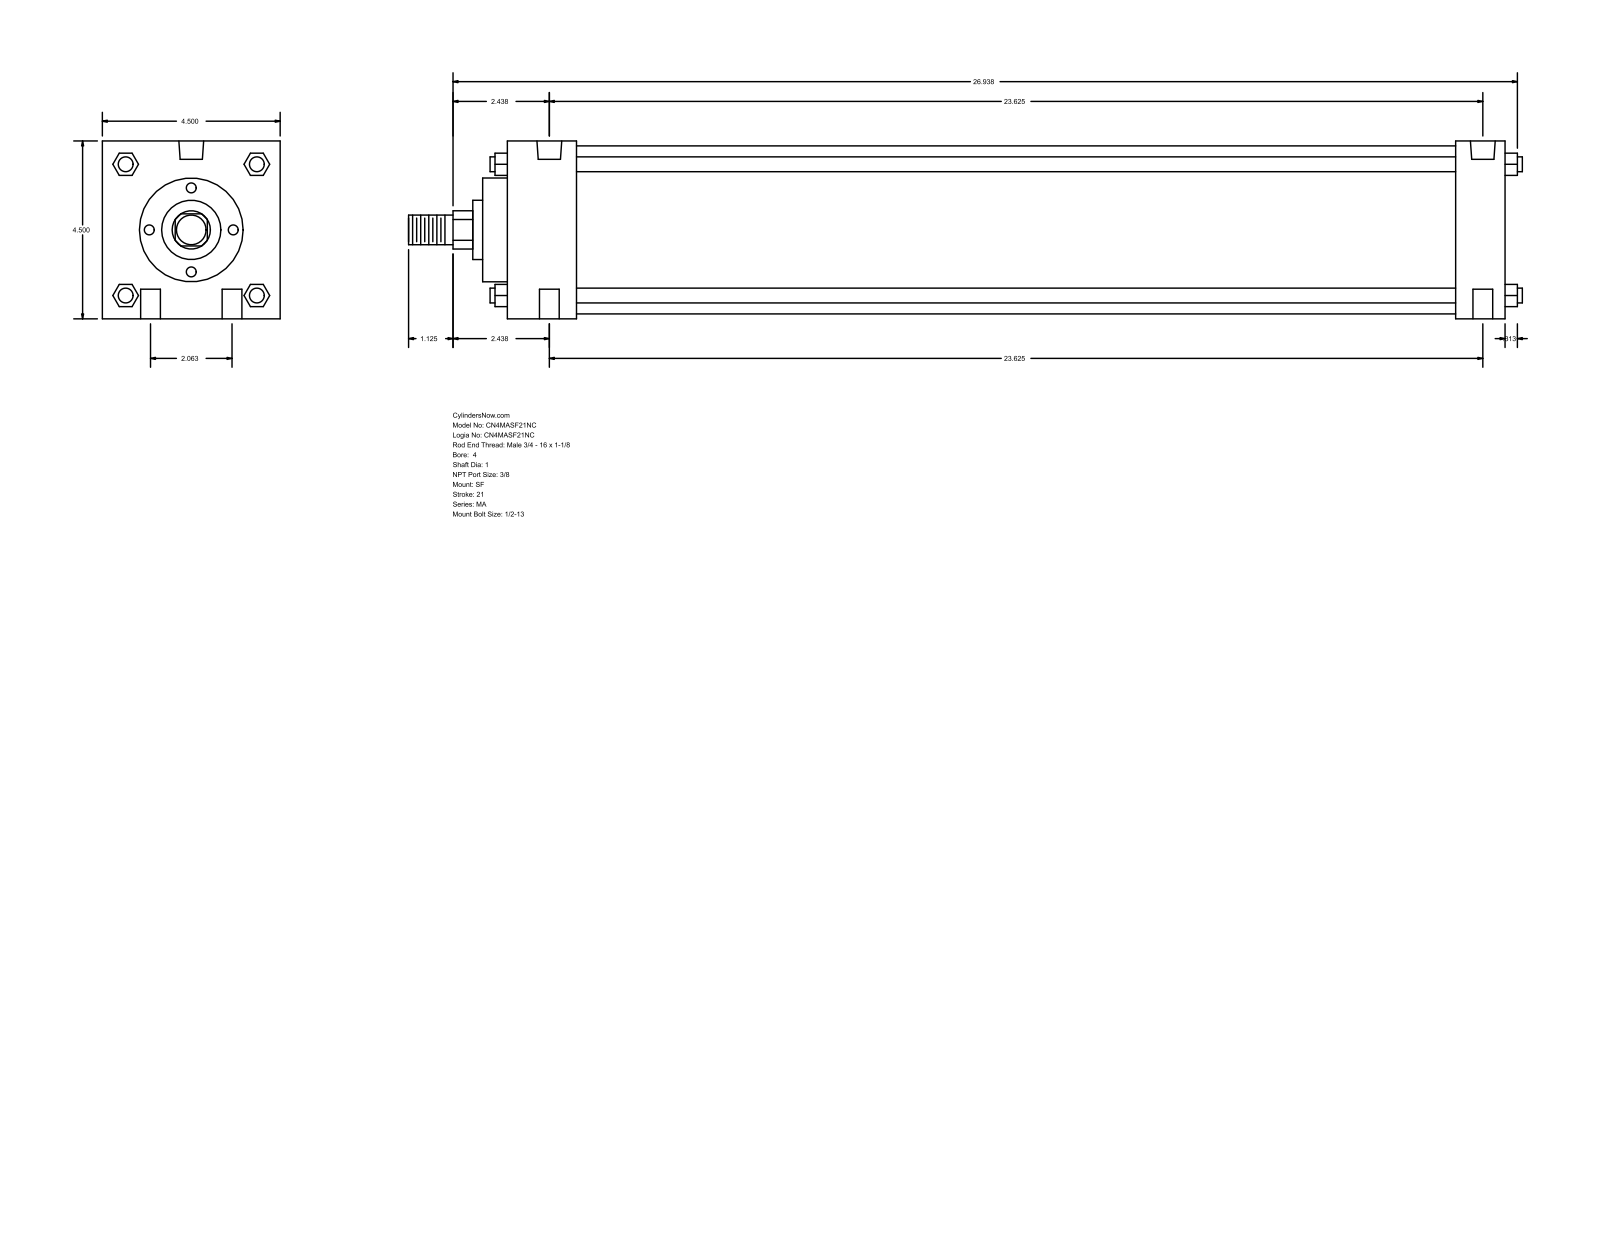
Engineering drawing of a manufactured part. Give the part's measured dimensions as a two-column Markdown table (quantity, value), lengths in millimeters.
| quantity | value |
| --- | --- |
| part name | MA_SF__0400_1 |
| STEP written by | GSSL Pune (CONFIG_CONTROL_DESIGN) |
| units | millimeters |
| bodies | 0 solids, 126 faces (95 planar, 31 cylindrical, 0 other) |
| overall size | 715.96 × 114.3 × 114.3 |
| round holes (diameter × count) | 12.7 × 4, 11.11 × 2, 15.93 × 2 |
| round bosses / shafts (diameter × count) | 9.53 × 4, 107.95 × 1, 66.67 × 1, 38.1 × 1, 25.4 × 1, 19.05 × 1 |
| partial cylindrical surfaces (radius × count) | 12.29 × 1 |
| main face-to-face distances | 114.3, 641.35, 609.6, 31.75, 44.46, 565.14, 596.89, 657.22, 15.87, 60.33 |
| hole center spacings | 26.19, 600.65, 600.08, 52.38, 602.36, 590.56 |
